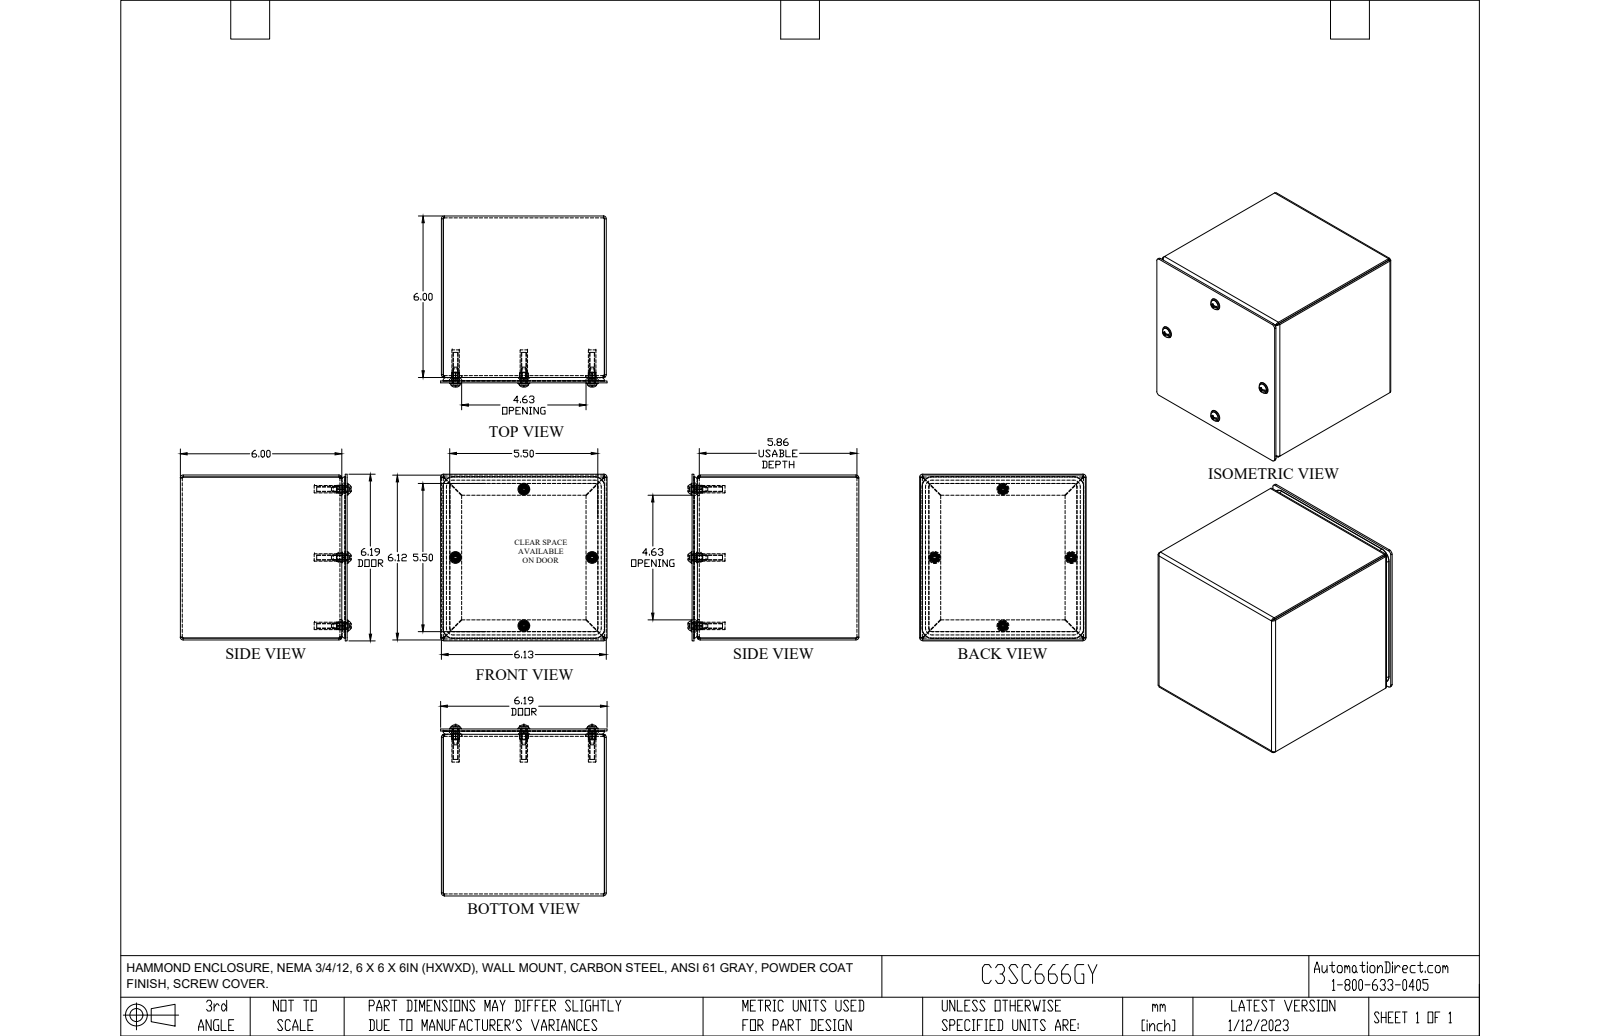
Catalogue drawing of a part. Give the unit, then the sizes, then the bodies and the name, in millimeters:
Units: millimetres
Overall size (bounding box): 161.2 × 157.2 × 157.2
Round holes (diameter × count): ⌀4 ×4, ⌀4.1 ×4, ⌀6.4 ×4
Round bosses / shafts (diameter × count): ⌀11.2 ×4, ⌀9.9 ×4, ⌀6.1 ×4, ⌀4.8 ×4, ⌀3.8 ×4, ⌀7 ×3, ⌀7 ×1
Partial cylindrical surfaces — rounded edges, fillets, slot ends (radius × count): R1 ×8, R2.8 ×8, R3.2 ×8, R3.2 ×4, R4.1 ×4, R9.5 ×4
Main face-to-face distances: 1.8, 153.8, 155.6, 152, 1.8, 155.6, 157.4, 153.8, 155.6, 150.6
Hole centre spacings: 91.2, 128.9
Volume: 280 400 mm³ · Surface area: 325 500 mm²
Bodies: 15 solids, 432 faces (260 planar, 92 cylindrical, 80 other)
Part name (STEP PRODUCT): C3SC666GY
STEP written by: SolidWorks 2021 (AUTOMOTIVE_DESIGN)
